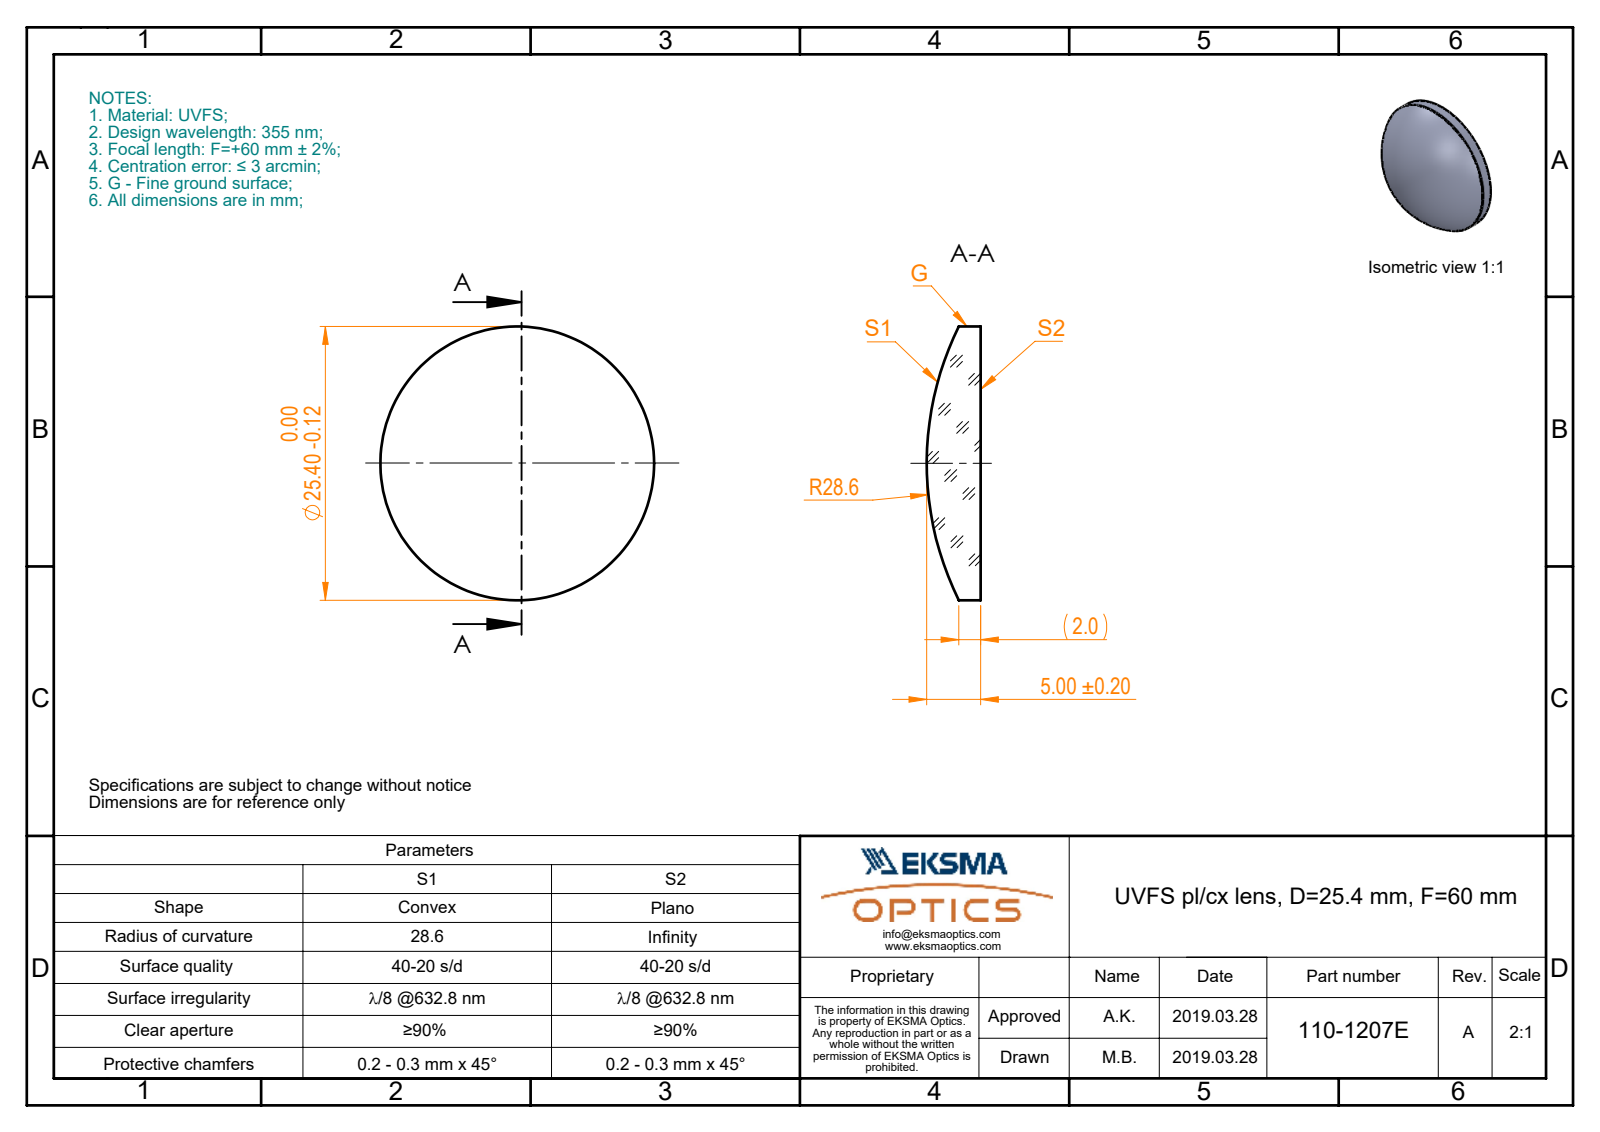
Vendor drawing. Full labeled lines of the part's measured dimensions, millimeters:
Part name (STEP PRODUCT): 110-1207E UVFS pl-cx 25.4 F60
STEP written by: SolidWorks 2017 (CONFIG_CONTROL_DESIGN)
Units: millimetres
Bodies: 1 solid, 5 faces (1 planar, 2 cylindrical, 2 other)
Overall size (bounding box): 25.4 × 25.4 × 5
Volume: 1 793 mm³ · Surface area: 1 203 mm²
Round bosses / shafts (diameter × count): ⌀25.4 ×1
